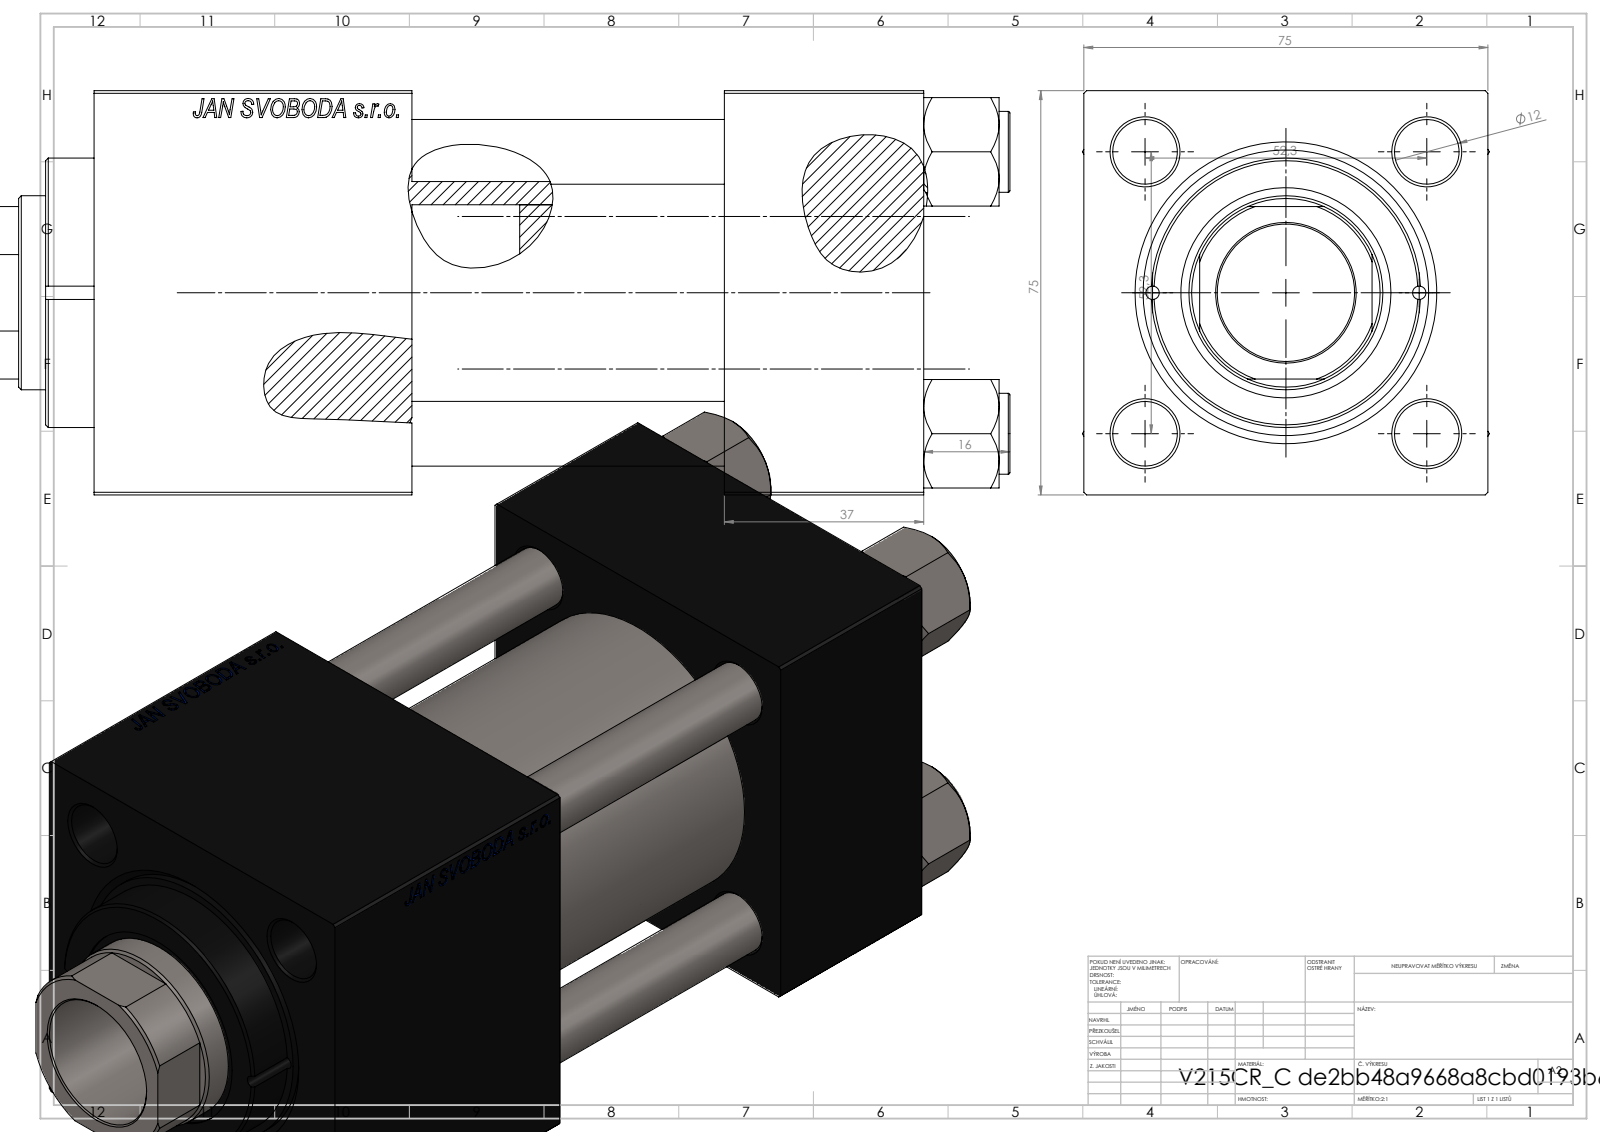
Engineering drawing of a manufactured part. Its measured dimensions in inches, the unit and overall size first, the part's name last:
Units: inches
Overall size (bounding box): 7.677 × 2.974 × 2.953
Round holes (diameter × count): ⌀0.472 ×4, ⌀0.098 ×2, ⌀0.276 ×2, ⌀0.825 ×2, ⌀1.181 ×2, ⌀1.004 ×1, ⌀1.417 ×1, ⌀1.535 ×1, ⌀1.614 ×1, ⌀2.087 ×1
Round bosses / shafts (diameter × count): ⌀0.591 ×4, ⌀2.205 ×1, ⌀1.969 ×1
Partial cylindrical surfaces — rounded edges, fillets, slot ends (radius × count): R0.689 ×1
Main face-to-face distances: 2.953, 1.457, 3.74, 2.283, 6.063, 4.606, 2.323, 4.933, 3.476, 1.193
Hole centre spacings: 1.031, 1.456, 2.059, 2.253, 0.974, 2.912, 1.949, 3.681
Volume: 41.86 in³ · Surface area: 241.2 in²
Bodies: 11 solids, 1154 faces (528 planar, 90 cylindrical, 536 other)
Part name (STEP PRODUCT): V215CR_C_TYCINKA; V215CR_VCP_C; NUT_M5_C; V215CR_C_Body (+1 more)
STEP written by: SolidWorks 2019 (CONFIG_CONTROL_DESIGN)
